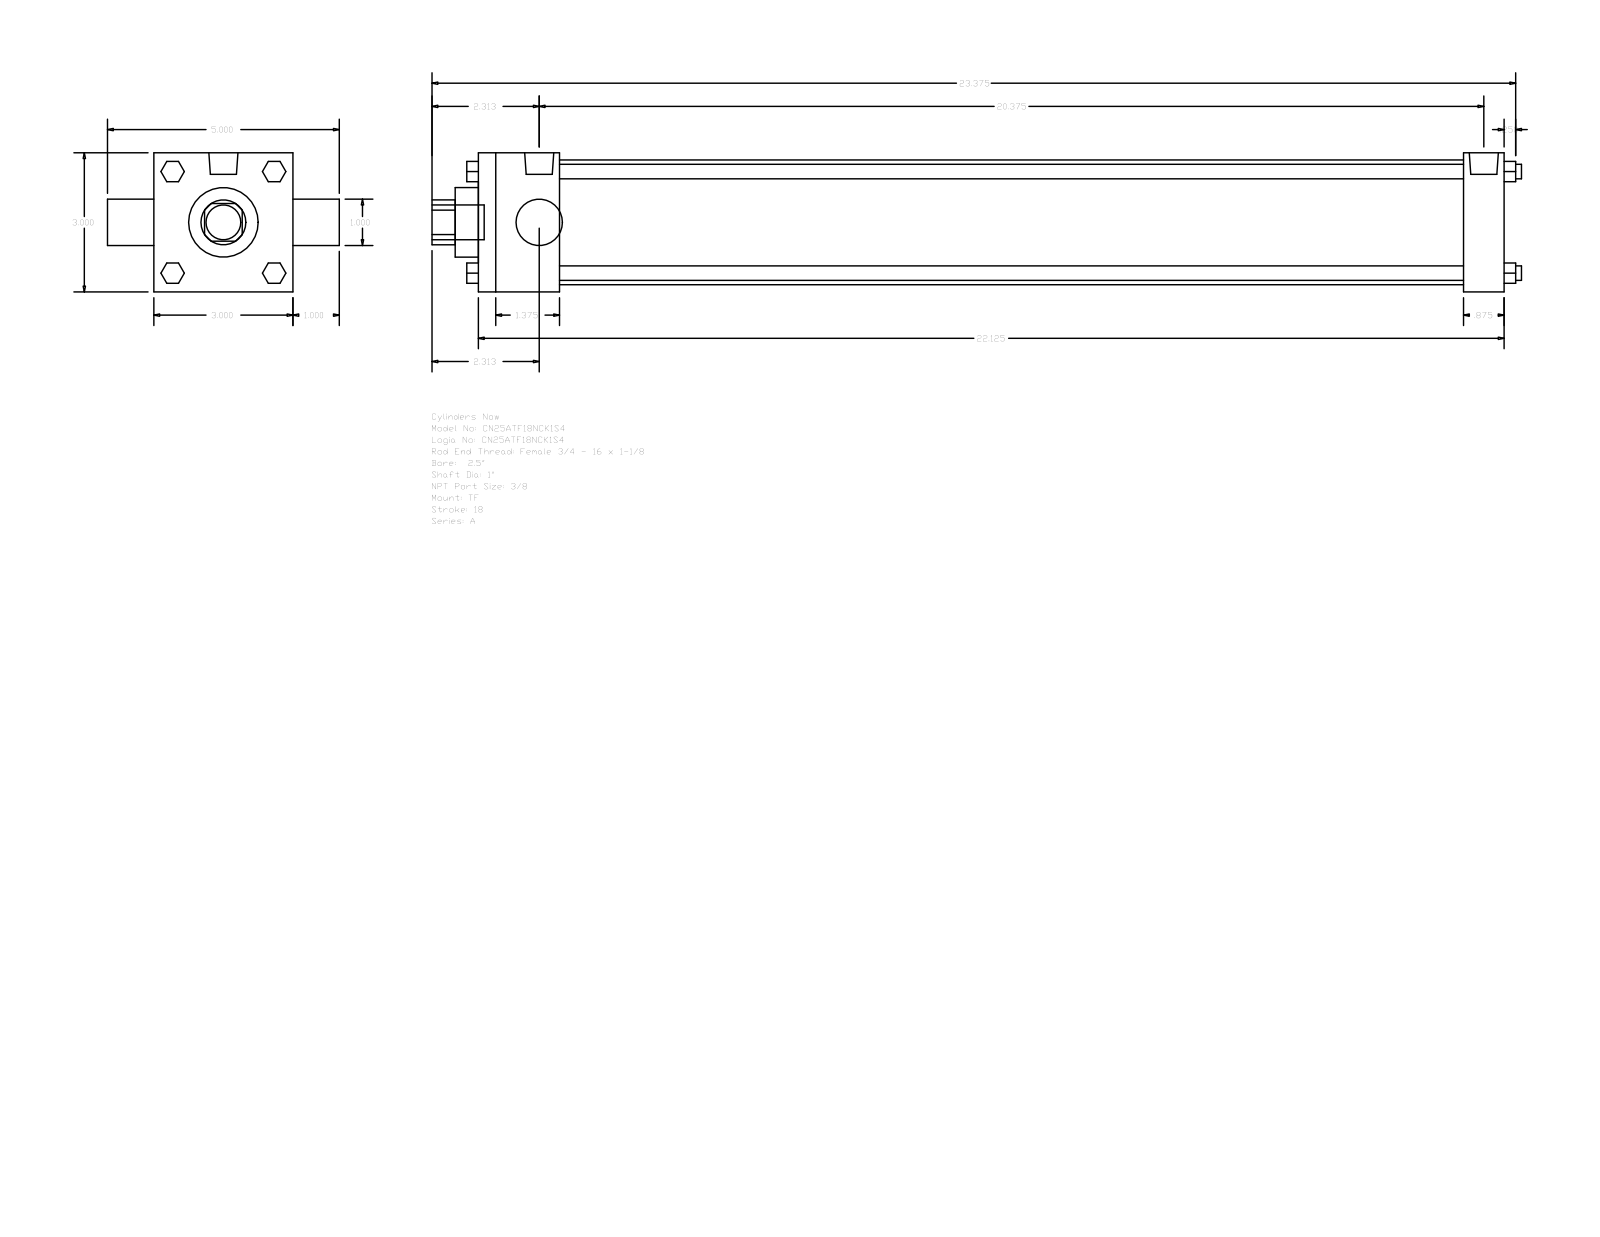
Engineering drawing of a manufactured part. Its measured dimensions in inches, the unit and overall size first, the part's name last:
Units: inches
Overall size (bounding box): 23.5 × 5 × 3
Round holes (diameter × count): ⌀1 ×2, ⌀1.5 ×1, ⌀2.69 ×1
Round bosses / shafts (diameter × count): ⌀0.313 ×4, ⌀0.219 ×3, ⌀0.627 ×2, ⌀0.75 ×1
Partial cylindrical surfaces — rounded edges, fillets, slot ends (radius × count): R0.484 ×1
Main face-to-face distances: 3, 22.125, 1.75, 21.25, 19.5, 20.375, 0.875, 1, 4, 22.625
Bodies: 0 solids, 120 faces (92 planar, 28 cylindrical, 0 other)
Part name (STEP PRODUCT): A_TF__0250_1
STEP written by: GSSL Pune (CONFIG_CONTROL_DESIGN)
